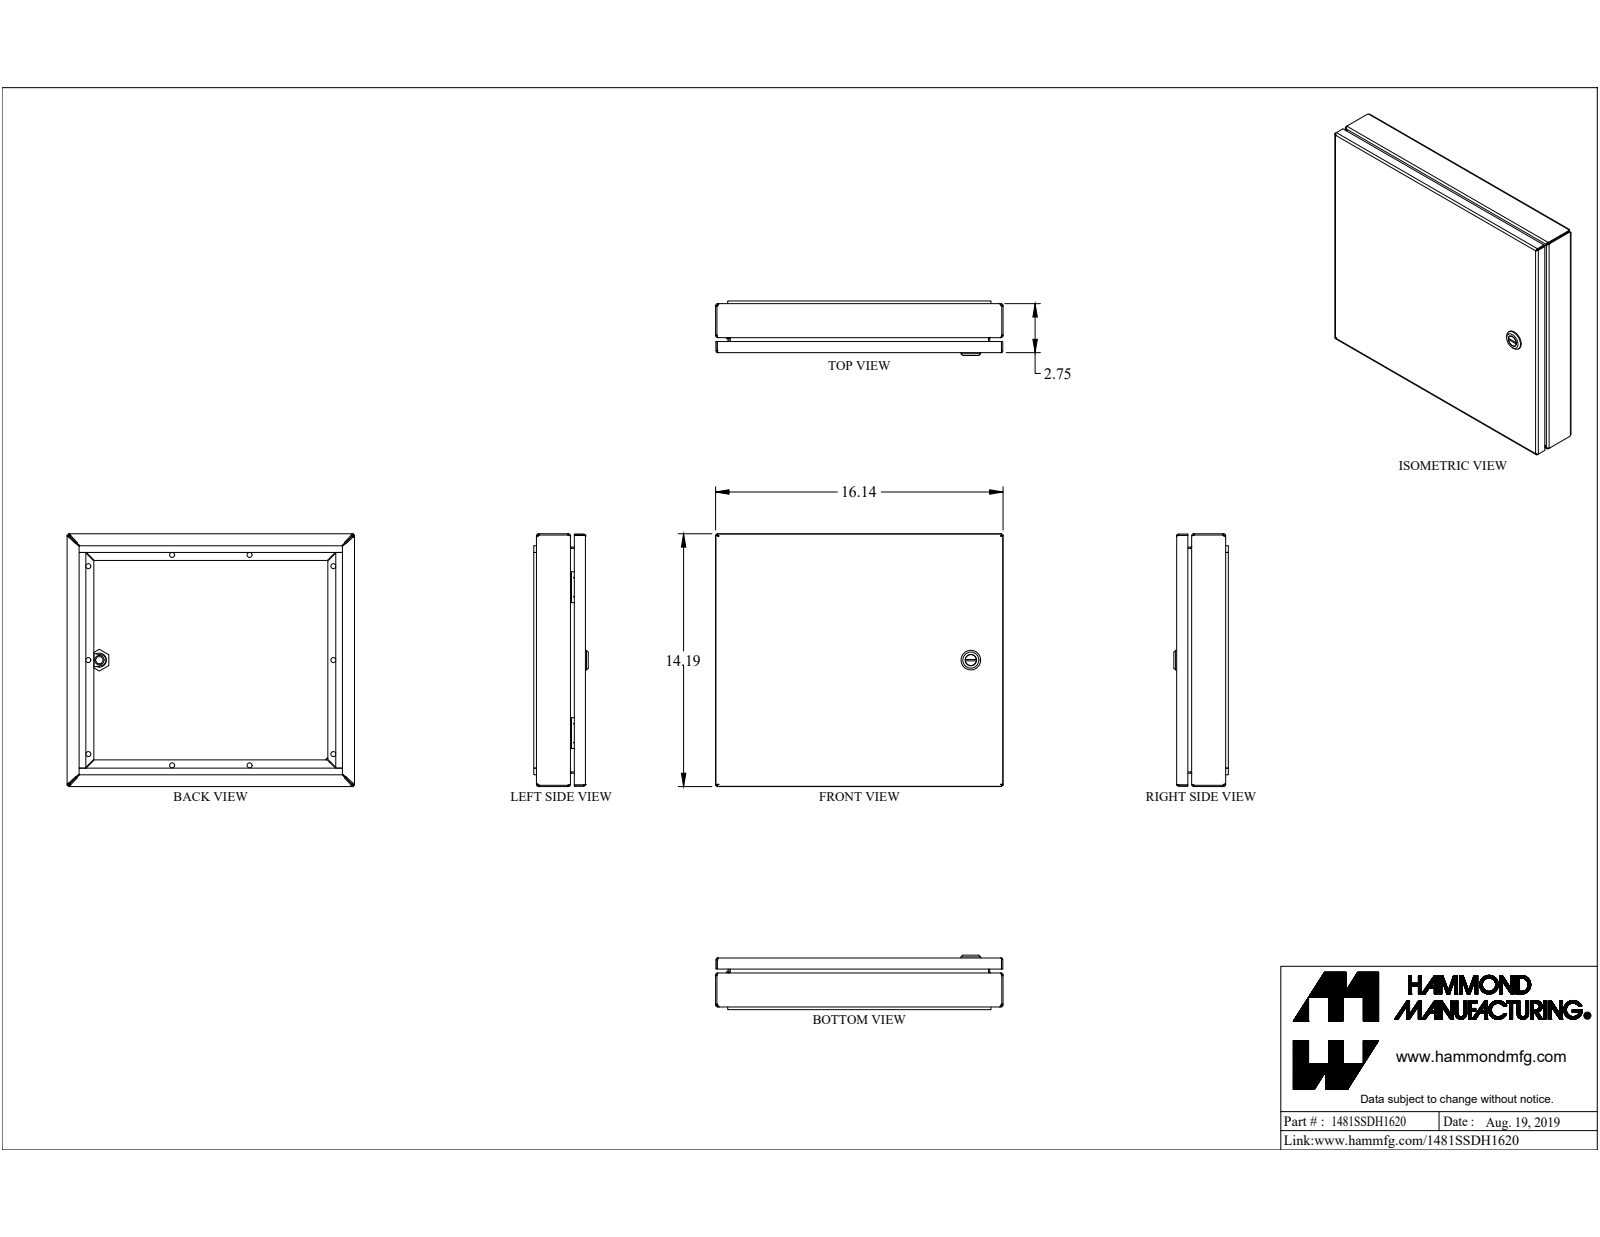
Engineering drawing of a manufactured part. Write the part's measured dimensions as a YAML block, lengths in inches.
part_name: "1481SSDH1620"
step_written_by: "SolidWorks 2019 (CONFIG_CONTROL_DESIGN)"
units: inches
bodies: {solids: 24, faces: 620, planar: 374, cylindrical: 149, other: 97}
overall_size: [16.14, 14.19, 3.06]
volume: 49.6
surface_area: 1294
round_holes:
  - {diameter: 0.281, count: 10}
  - {diameter: 0.172, count: 1}
  - {diameter: 0.197, count: 1}
  - {diameter: 0.24, count: 1}
  - {diameter: 0.242, count: 1}
  - {diameter: 0.387, count: 1}
  - {diameter: 0.5, count: 1}
  - {diameter: 0.63, count: 1}
  - {diameter: 0.768, count: 1}
round_bosses_or_shafts:
  - {diameter: 1.1, count: 1}
  - {diameter: 0.785, count: 1}
  - {diameter: 0.625, count: 1}
  - {diameter: 0.525, count: 1}
  - {diameter: 0.475, count: 1}
  - {diameter: 0.398, count: 1}
  - {diameter: 0.356, count: 1}
  - {diameter: 0.313, count: 1}
partial_cylinders:
  - {radius: 0.036, count: 28}
  - {radius: 0.108, count: 28}
  - {radius: 0.006, count: 4}
  - {radius: 0.062, count: 4}
  - {radius: 0.25, count: 4}
  - {radius: 0.499, count: 4}
  - {radius: 0.125, count: 2}
  - {radius: 0.021, count: 1}
face_to_face_distances: [0.072, 2.578, 0.842, 1.736, 2.65, 14.118, 16.068, 2.506, 2.678, 1.836]
hole_center_spacings: [4.75, 5.273, 7.554, 9.078, 10.813, 12.131, 14.388, 14.739]
